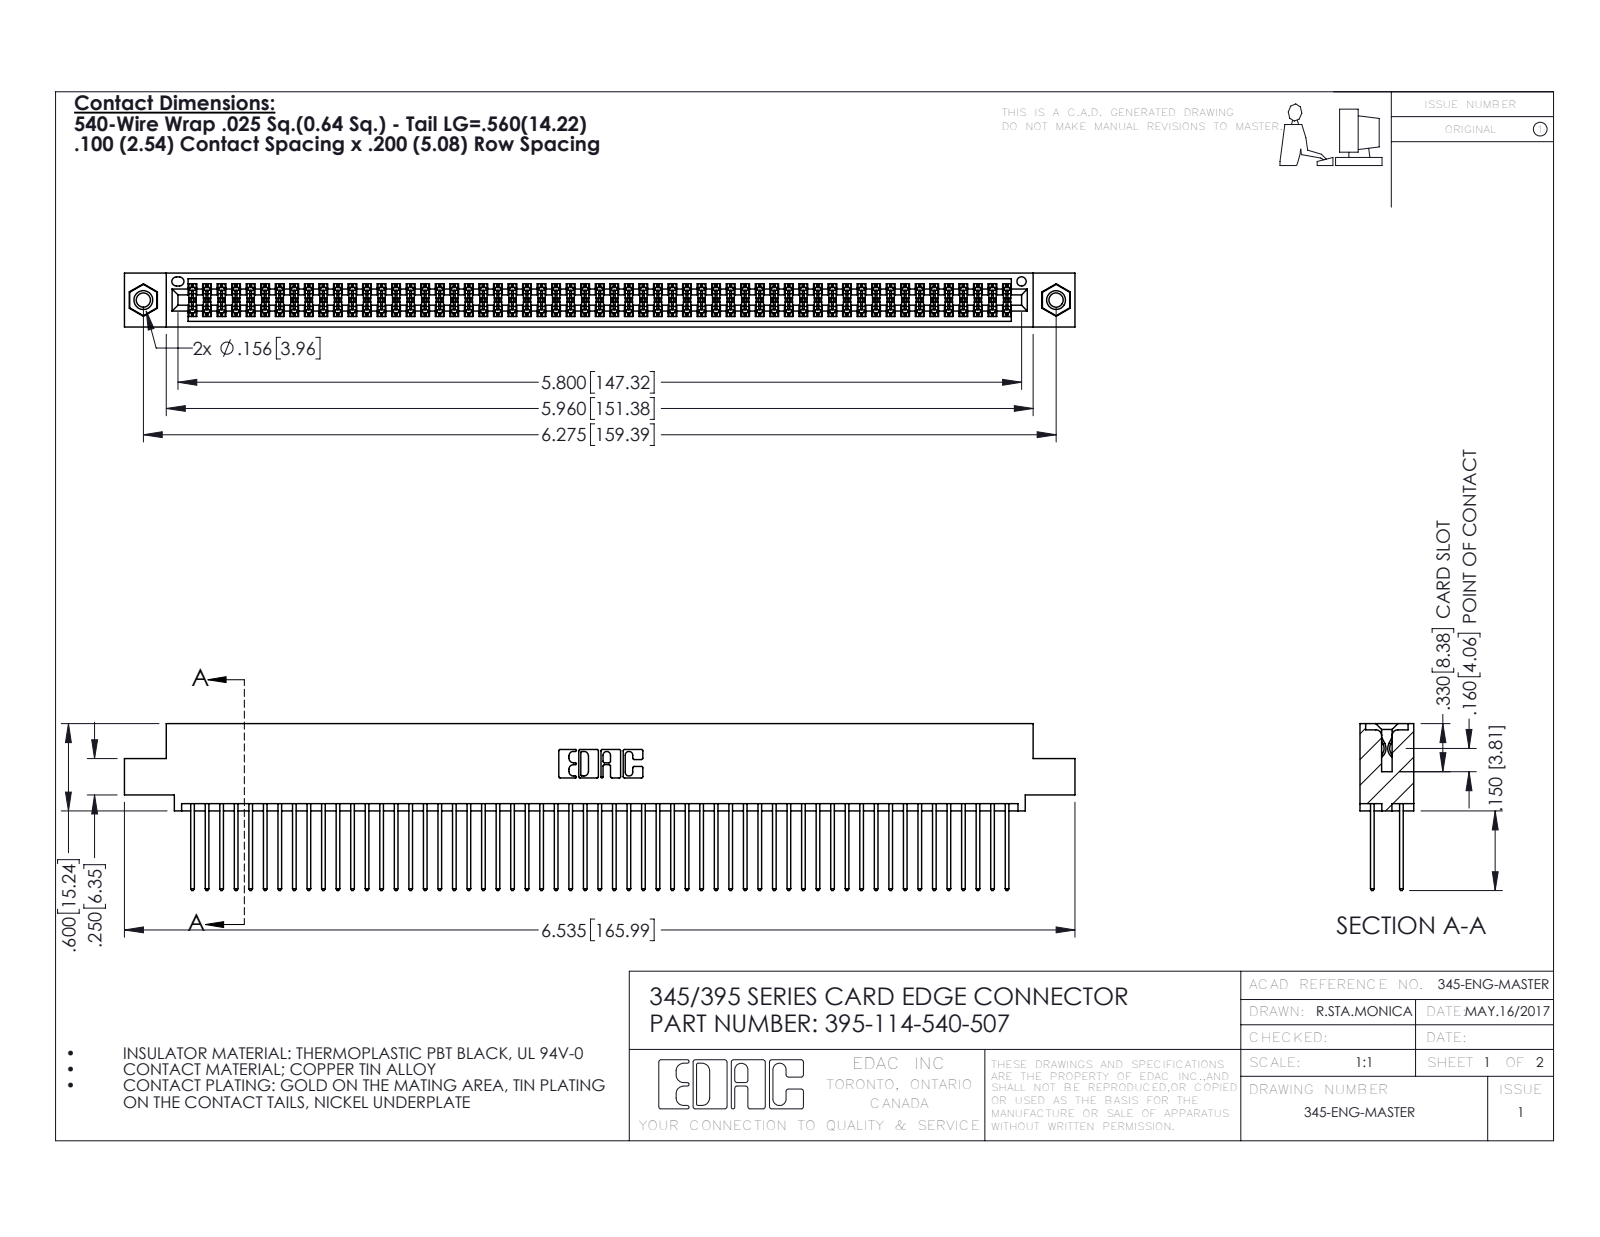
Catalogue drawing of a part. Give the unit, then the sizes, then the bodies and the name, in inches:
Units: inches
Overall size (bounding box): 6.535 × 1.147 × 0.37
Round holes (diameter × count): ⌀0.098 ×2, ⌀0.125 ×2, ⌀0.156 ×2, ⌀0.064 ×1
Round bosses / shafts (diameter × count): ⌀0.155 ×2
Partial cylindrical surfaces — rounded edges, fillets, slot ends (radius × count): R0.006 ×171, R0.01 ×114, R0.01 ×22, R0.007 ×6, R0.031 ×6, R0.026 ×3, R0.014 ×2, R0.019 ×2
Main face-to-face distances: 0.072, 0.298, 0.2, 0.098, 0.272, 0.025, 0.37, 0.225, 0.175, 0.149
Hole centre spacings: 0.27, 6.039, 6.275
Volume: 1.014 in³ · Surface area: 41.8 in²
Bodies: 117 solids, 5890 faces (3878 planar, 1996 cylindrical, 16 other)
Part name (STEP PRODUCT): 395-114-540-507; 345-250-001_345-250-005-103; 345 Part_0.110 Offset - 0.156 Dia-TI; 345-292-001_345-293-140
STEP written by: SolidWorks 2016 (CONFIG_CONTROL_DESIGN)
